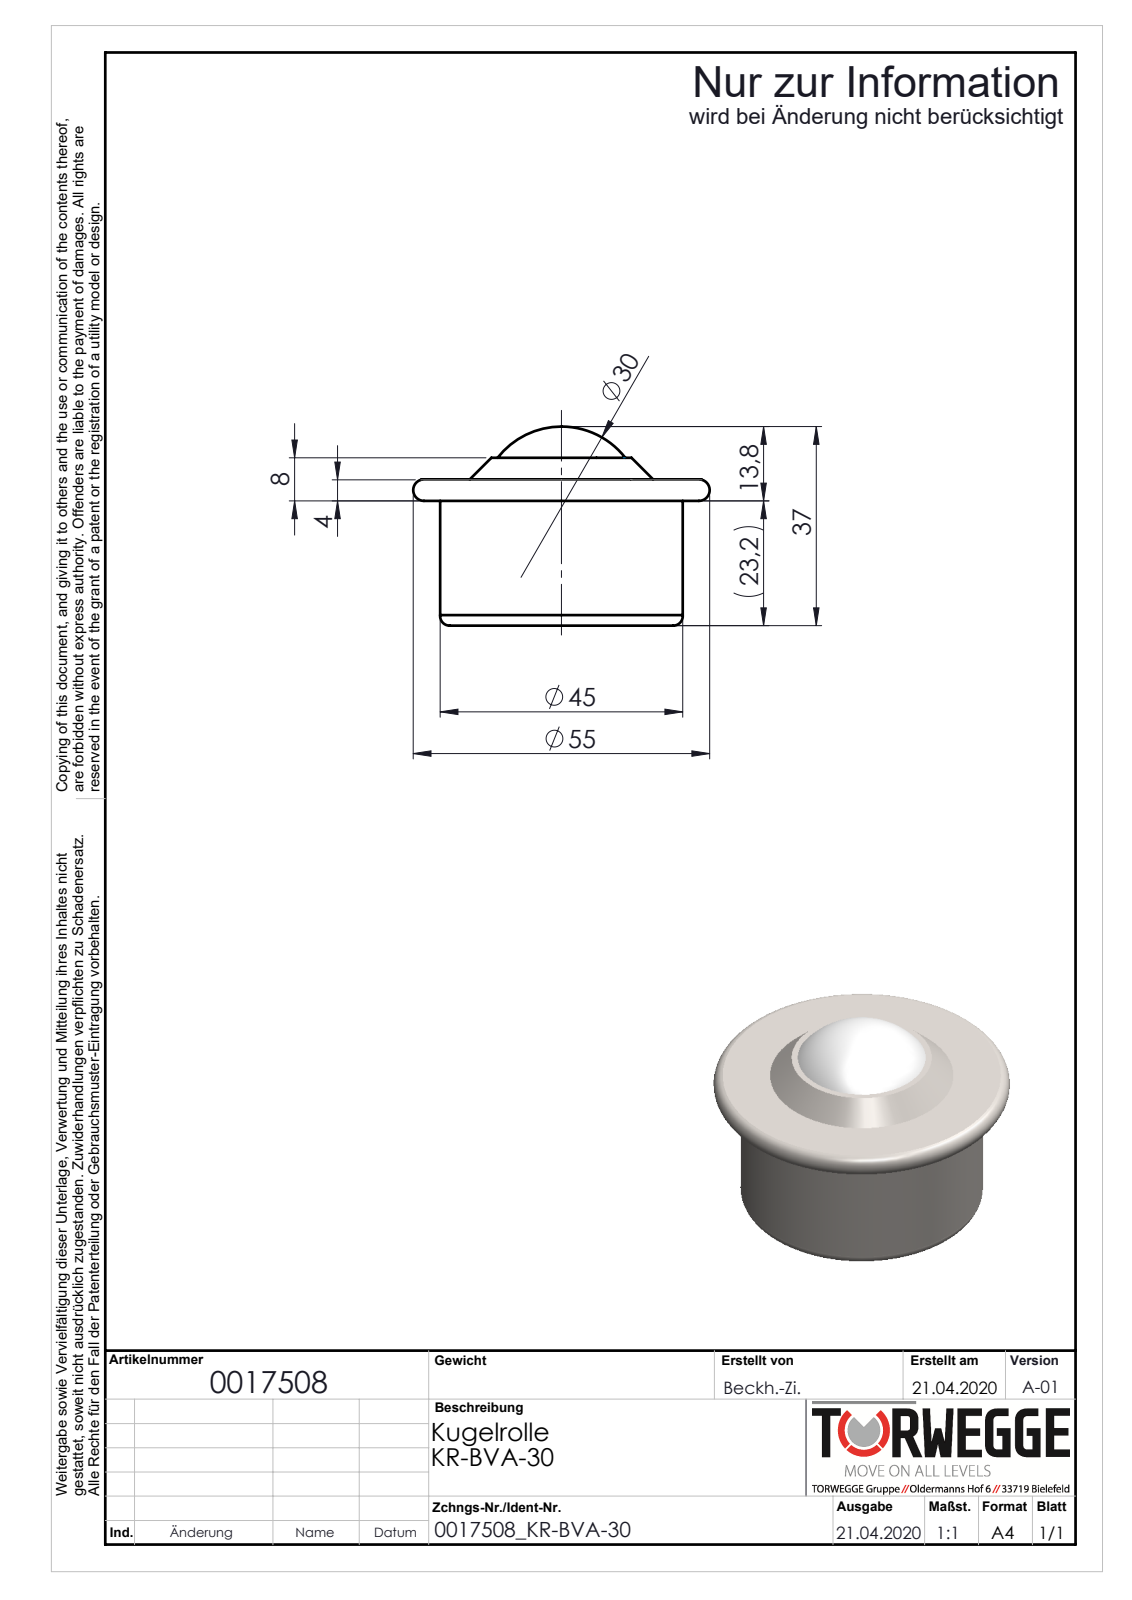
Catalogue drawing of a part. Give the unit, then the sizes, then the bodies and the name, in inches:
Units: inches
Overall size (bounding box): 2.165 × 2.165 × 1.455
Round holes (diameter × count): ⌀0.098 ×1, ⌀0.394 ×1
Round bosses / shafts (diameter × count): ⌀1.772 ×1
Main face-to-face distances: 0.157, 0.315
Bodies: 0 solids, 43 faces (4 planar, 6 cylindrical, 33 other)
Part name (STEP PRODUCT): 0017508
STEP written by: SolidWorks 2018 (AUTOMOTIVE_DESIGN)
